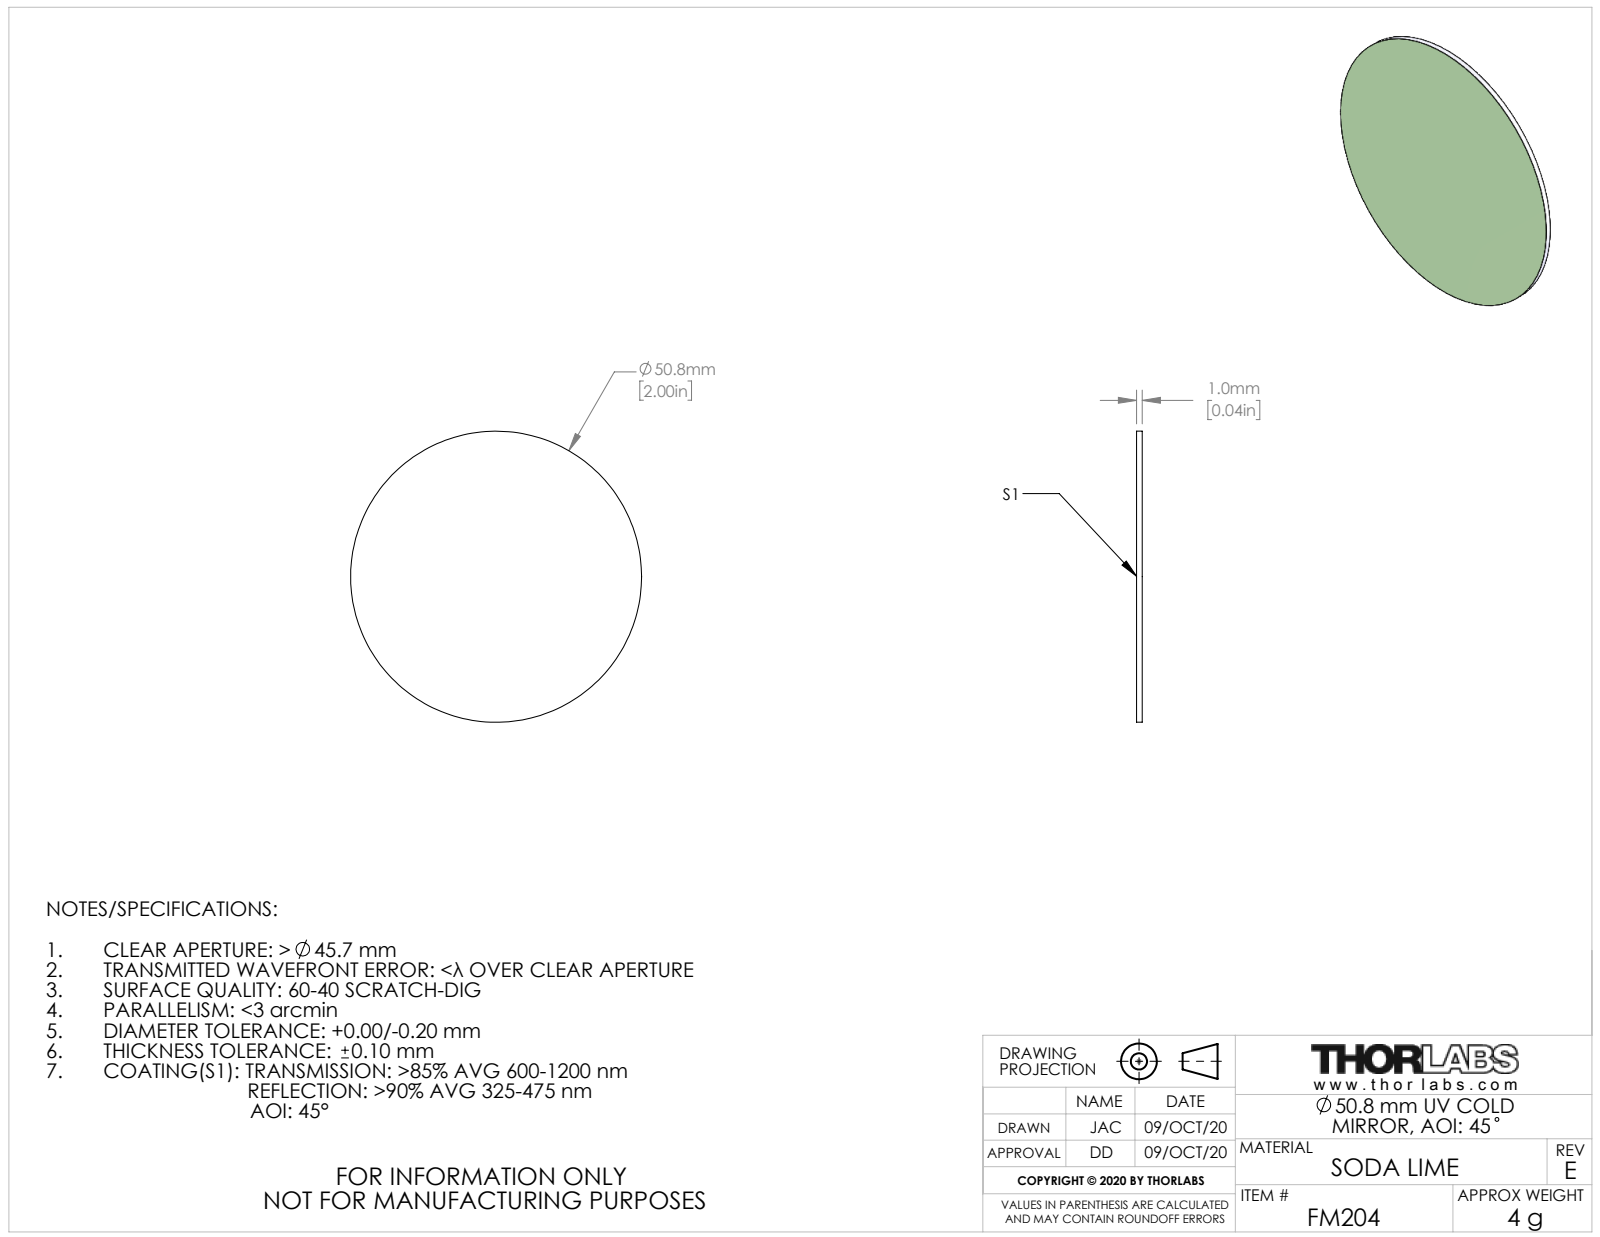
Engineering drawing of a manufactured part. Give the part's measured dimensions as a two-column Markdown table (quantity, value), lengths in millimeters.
| quantity | value |
| --- | --- |
| part name | 10646-E0W |
| STEP written by | SolidWorks 2018 (CONFIG_CONTROL_DESIGN) |
| units | millimeters |
| bodies | 1 solid, 4 faces (2 planar, 2 cylindrical, 0 other) |
| overall size | 50.8 × 50.8 × 1 |
| volume | 2 027 mm³ |
| surface area | 4 213 mm² |
| round bosses / shafts (diameter × count) | 50.8 × 1 |
| main face-to-face distances | 1 |
